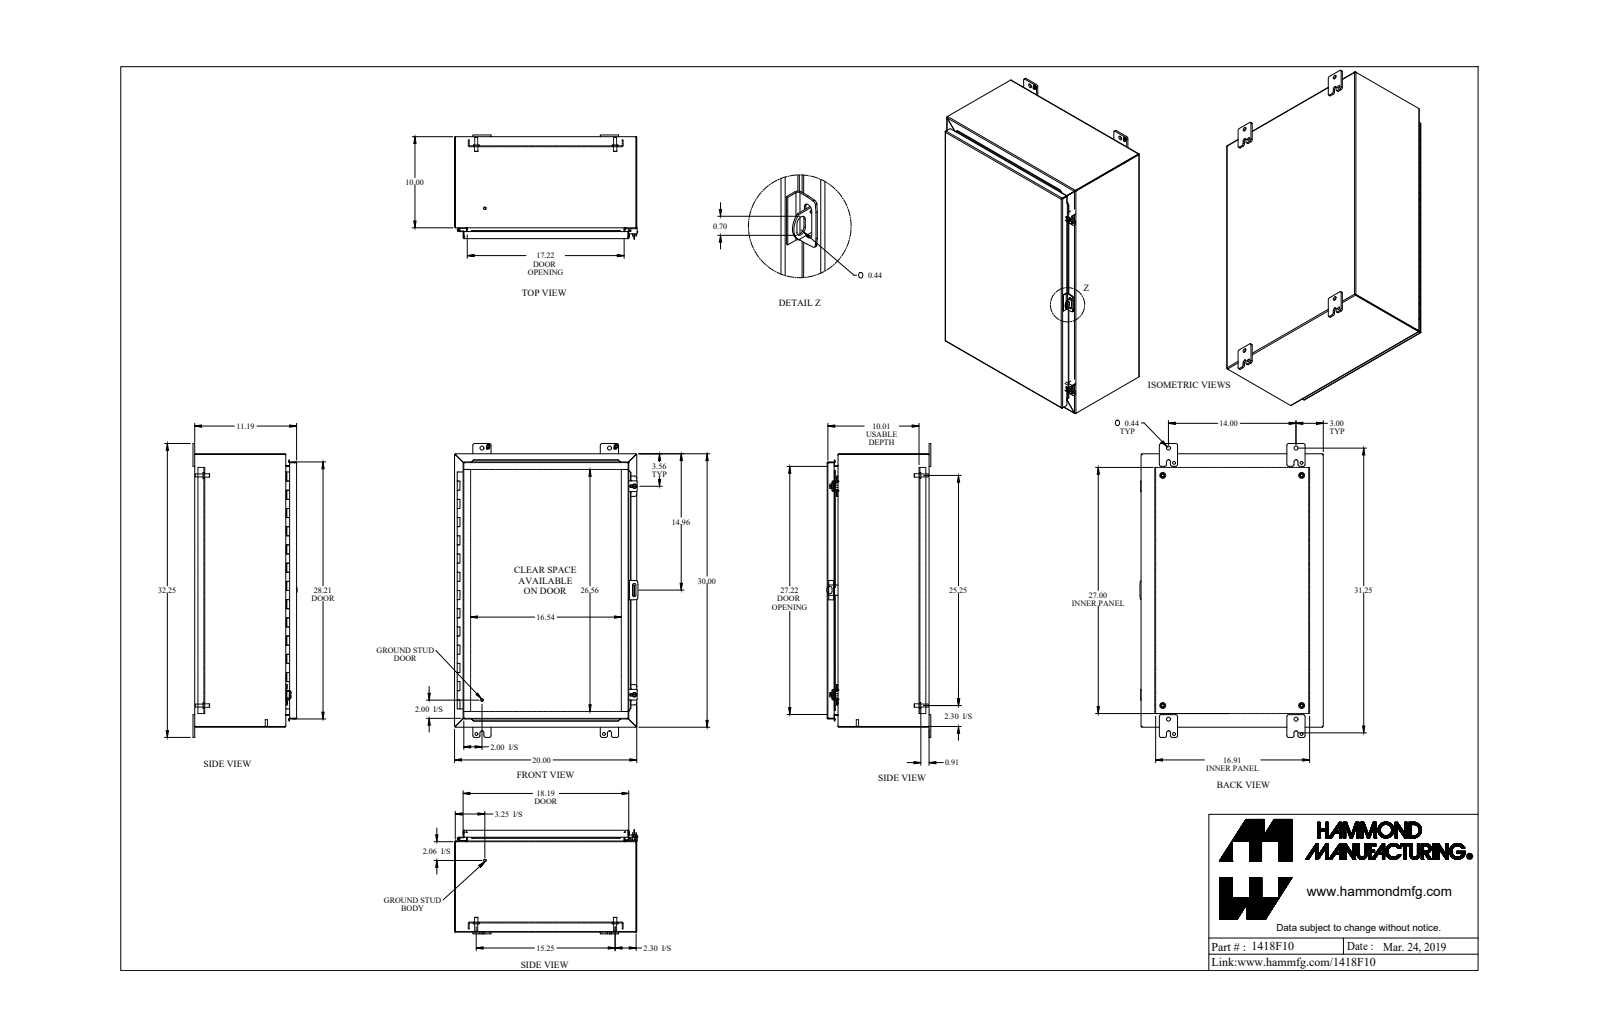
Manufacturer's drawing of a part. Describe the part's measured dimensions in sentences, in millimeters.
The part is named "1418F10". Its 3-D file was written by "SolidWorks 2019 (AUTOMOTIVE_DESIGN)". It is 38 solids with 1046 faces: 717 planar, 275 cylindrical and 54 other. Overall it measures 819.2 by 511.2 by 290.5 millimeters. Its volume is 3 985 000 cubic millimeters and its surface area 4 083 000 square millimeters. Round holes: 4 of diameter 8, 4 of diameter 11.1, 4 of diameter 12.7, 2 of diameter 5.4, 2 of diameter 6.7, 2 of diameter 7.8, 2 of diameter 9.5, 2 of diameter 11.3, 1 of diameter 3.2, 1 of diameter 4.7. Round bosses or shafts: 4 of diameter 16.5, 4 of diameter 9.5, 4 of diameter 8.4, 2 of diameter 25.4, 2 of diameter 12.7, 2 of diameter 9.9, 2 of diameter 7.1, 2 of diameter 6.4. Partial cylindrical surfaces (rounded edges, fillets, slot ends): 26 of radius 4.8, 20 of radius 0.9, 20 of radius 2.7, 13 of radius 1.2, 13 of radius 3.6, 8 of radius 0.2, 8 of radius 1.1, 8 of radius 2. The main face-to-face distances are 1.8, 282.3, 280.4, 506.2, 23.8, 284.1, 2.4, 25.6, 256.1, 254.2. The hole center spacings are 44.1, 355.6, 387.4, 755.7, 835.2, 749.2, 749.2, 753.9.
